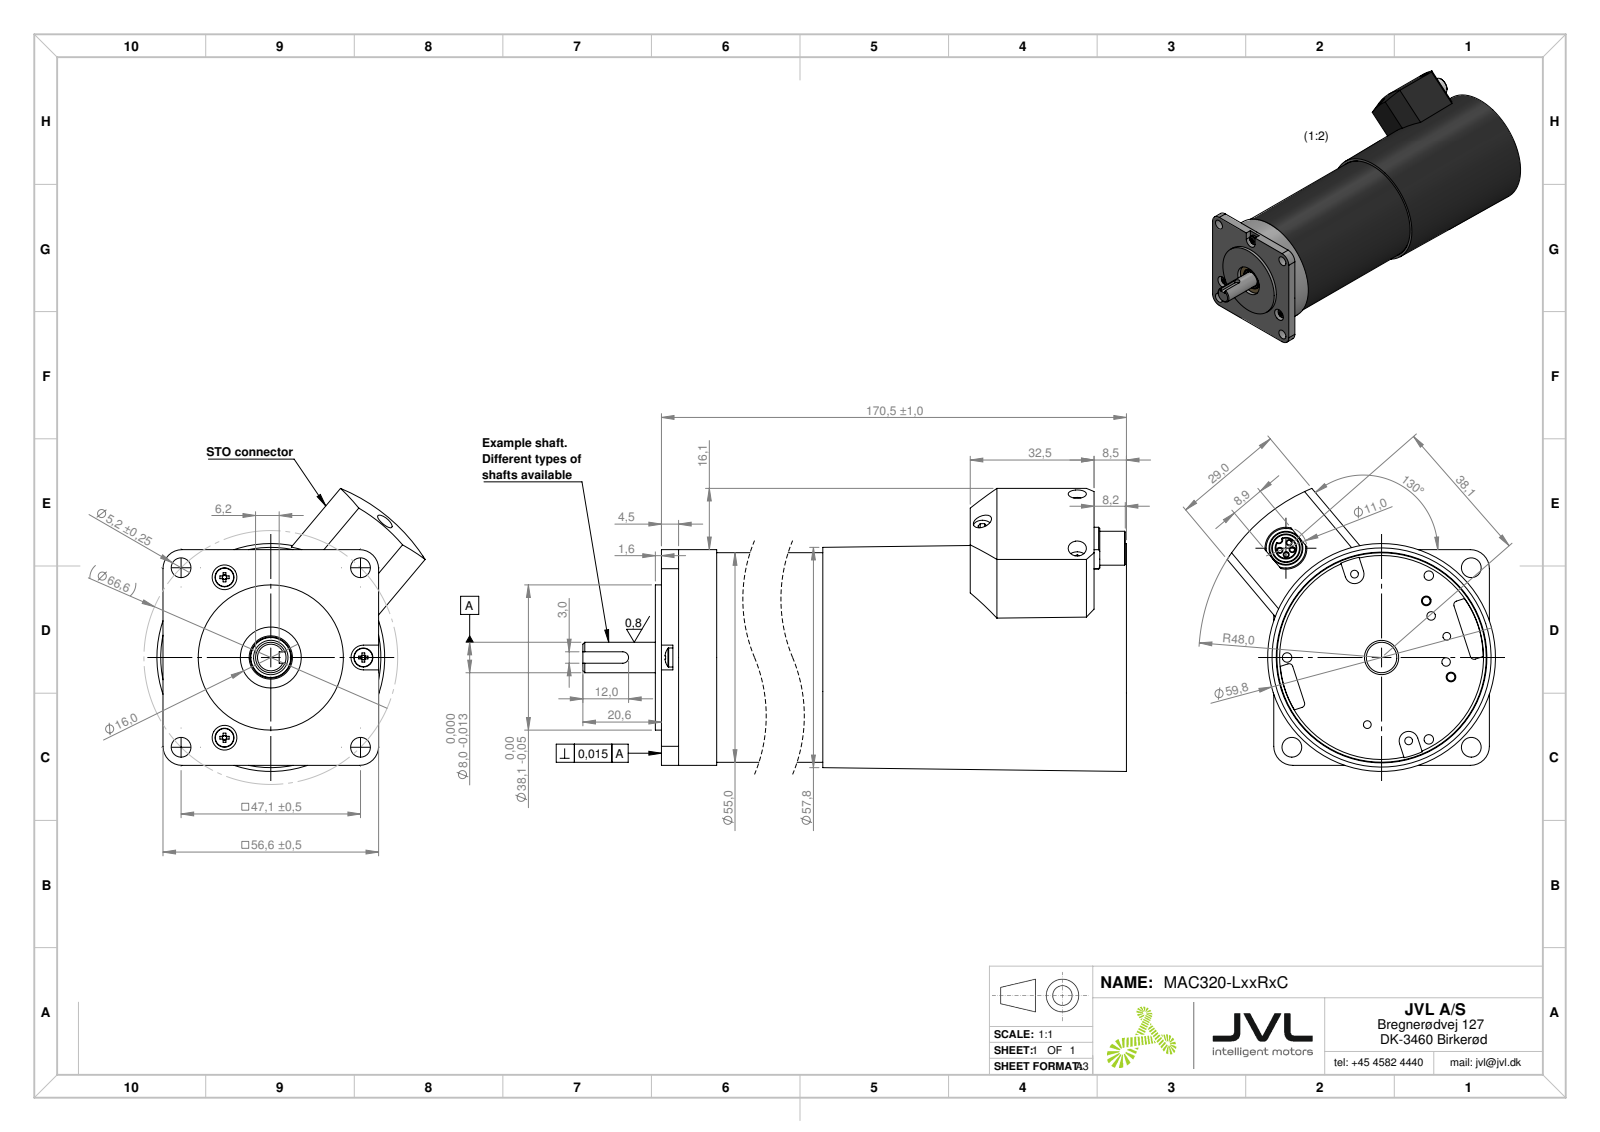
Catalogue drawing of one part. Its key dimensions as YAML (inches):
part_name: "MAC050-320-MTRBASE-mockup_MAC141-320; MAC050-320-HOUSE-mockup (MM0315)_DEFAULT; MAC050-320-SHAFT-mockup_4) Ø8 L20.6 Key:3-1.8-12 (MAC050-320); MAC050-320-STO-mockup (+6 more)"
step_written_by: "SolidWorks 2023 (AUTOMOTIVE_DESIGN)"
units: inches
bodies: {solids: 21, faces: 891, planar: 275, cylindrical: 263, other: 353}
overall_size: [7.756, 2.917, 2.767]
volume: 7.618
surface_area: 134
round_holes:
  - {diameter: 0.081, count: 6}
  - {diameter: 0.047, count: 4}
  - {diameter: 0.205, count: 4}
  - {diameter: 0.098, count: 3}
  - {diameter: 0.189, count: 3}
  - {diameter: 0.244, count: 3}
  - {diameter: 0.079, count: 1}
  - {diameter: 0.28, count: 1}
  - {diameter: 0.315, count: 1}
  - {diameter: 0.354, count: 1}
  - {diameter: 0.394, count: 1}
  - {diameter: 0.424, count: 1}
round_bosses_or_shafts:
  - {diameter: 0.098, count: 3}
  - {diameter: 0.089, count: 2}
  - {diameter: 2.228, count: 1}
  - {diameter: 2.165, count: 1}
  - {diameter: 1.5, count: 1}
  - {diameter: 1.102, count: 1}
  - {diameter: 0.866, count: 1}
  - {diameter: 0.688, count: 1}
partial_cylinders:
  - {radius: 0.009, count: 36}
  - {radius: 0.008, count: 10}
  - {radius: 0.039, count: 4}
  - {radius: 0.197, count: 4}
  - {radius: 0.004, count: 2}
  - {radius: 0.098, count: 2}
  - {radius: 0.157, count: 2}
  - {radius: 0.031, count: 1}
face_to_face_distances: [4.531, 4.713, 0.181, 0.236, 4.295, 4.476, 4.776, 4.539, 0.244, 0.063]
hole_center_spacings: [1.311, 1.854, 0.026, 0.957, 0.976, 1.682, 0.066, 0.067]
